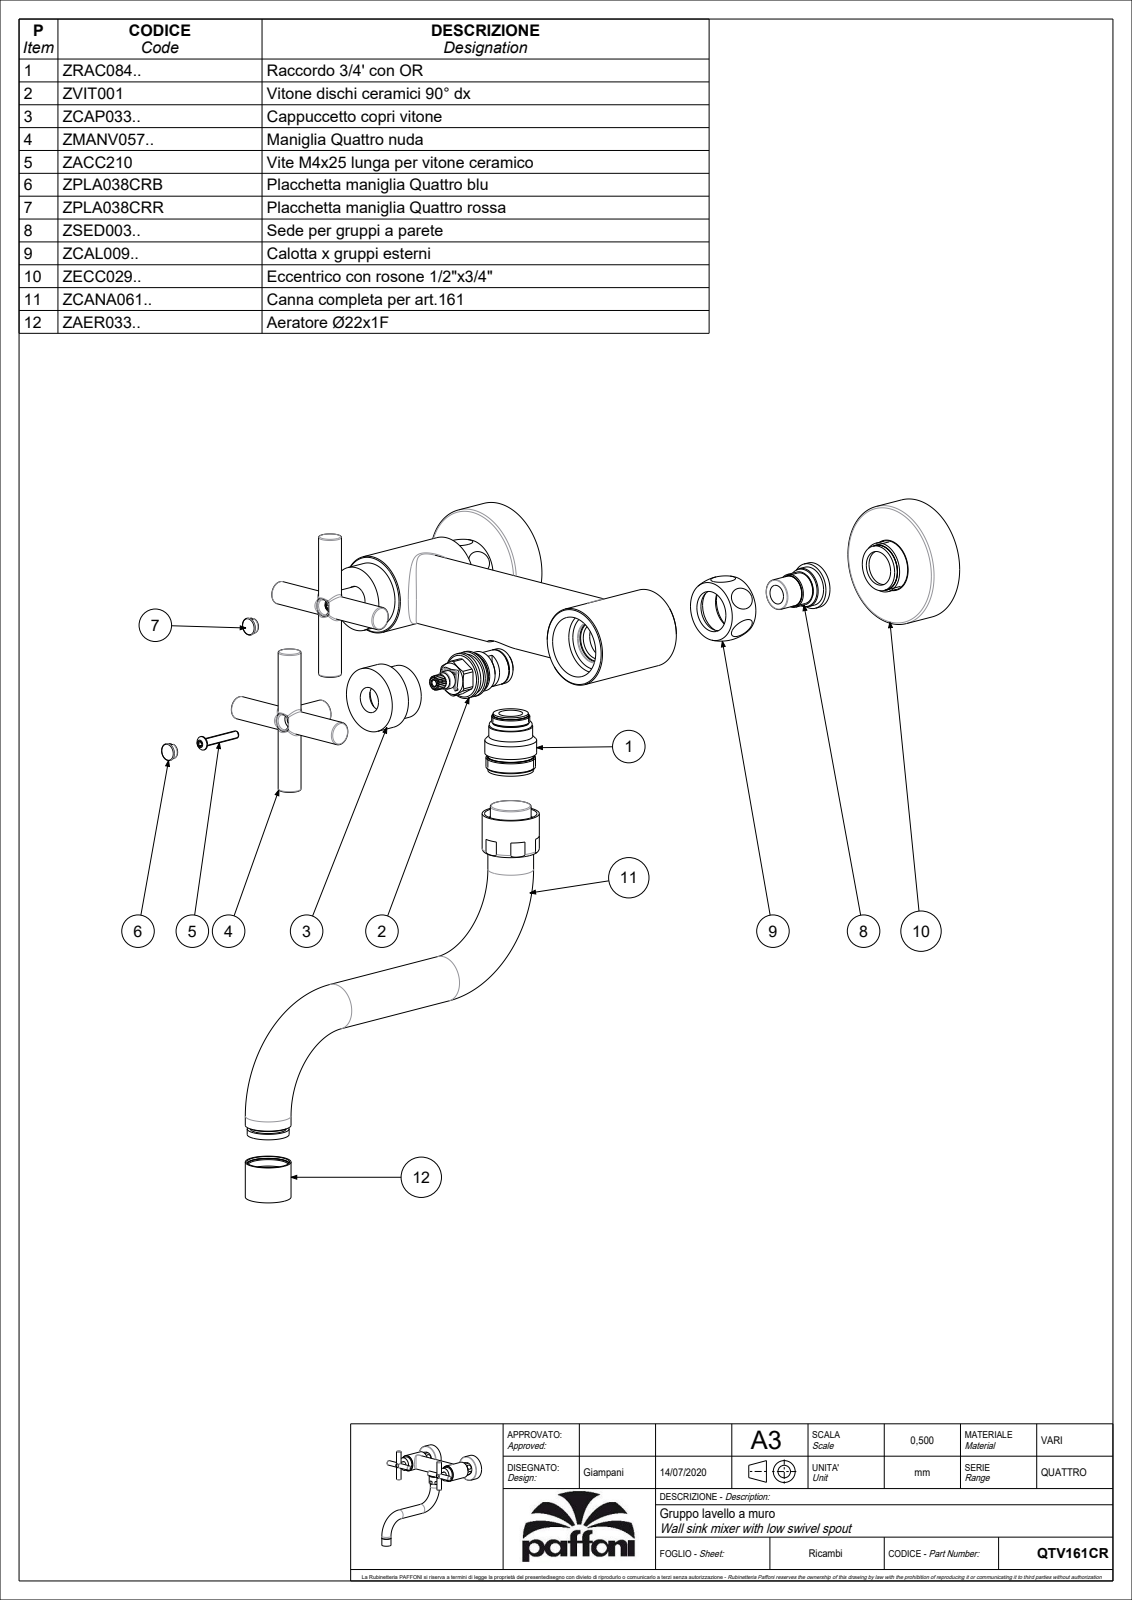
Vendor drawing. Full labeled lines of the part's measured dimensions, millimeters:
Part name (STEP PRODUCT): QTV161CR
STEP written by: CREO PARAMETRIC BY PTC INC, 2020044 (CONFIG_CONTROL_DESIGN)
Units: millimetres
Bodies: 4 solids, 2418 faces (1876 planar, 296 cylindrical, 246 other)
Overall size (bounding box): 258.4 × 225 × 214
Volume: 259 026 mm³ · Surface area: 165 315 mm²
Round holes (diameter × count): ⌀22 ×3, ⌀27.5 ×3, ⌀3.3 ×2, ⌀4.5 ×2, ⌀7 ×2, ⌀8 ×2, ⌀8.8 ×2, ⌀9.5 ×2, ⌀10 ×2, ⌀13.5 ×2, ⌀16.3 ×2, ⌀16.7 ×2
Round bosses / shafts (diameter × count): ⌀24 ×5, ⌀12 ×3, ⌀63.5 ×2, ⌀41 ×2, ⌀27 ×2, ⌀20.5 ×2, ⌀18.6 ×2, ⌀17.6 ×2
Partial cylindrical surfaces — rounded edges, fillets, slot ends (radius × count): R0.1 ×34, R0.5 ×4, R1 ×4, R3 ×2, R9.4 ×2, R5.3 ×1
Main face-to-face distances: 0.6, 10, 67.8, 18.5, 28.5, 19.1, 57.8, 11, 86.9, 86.3
Hole centre spacings: 126.44, 150, 180
